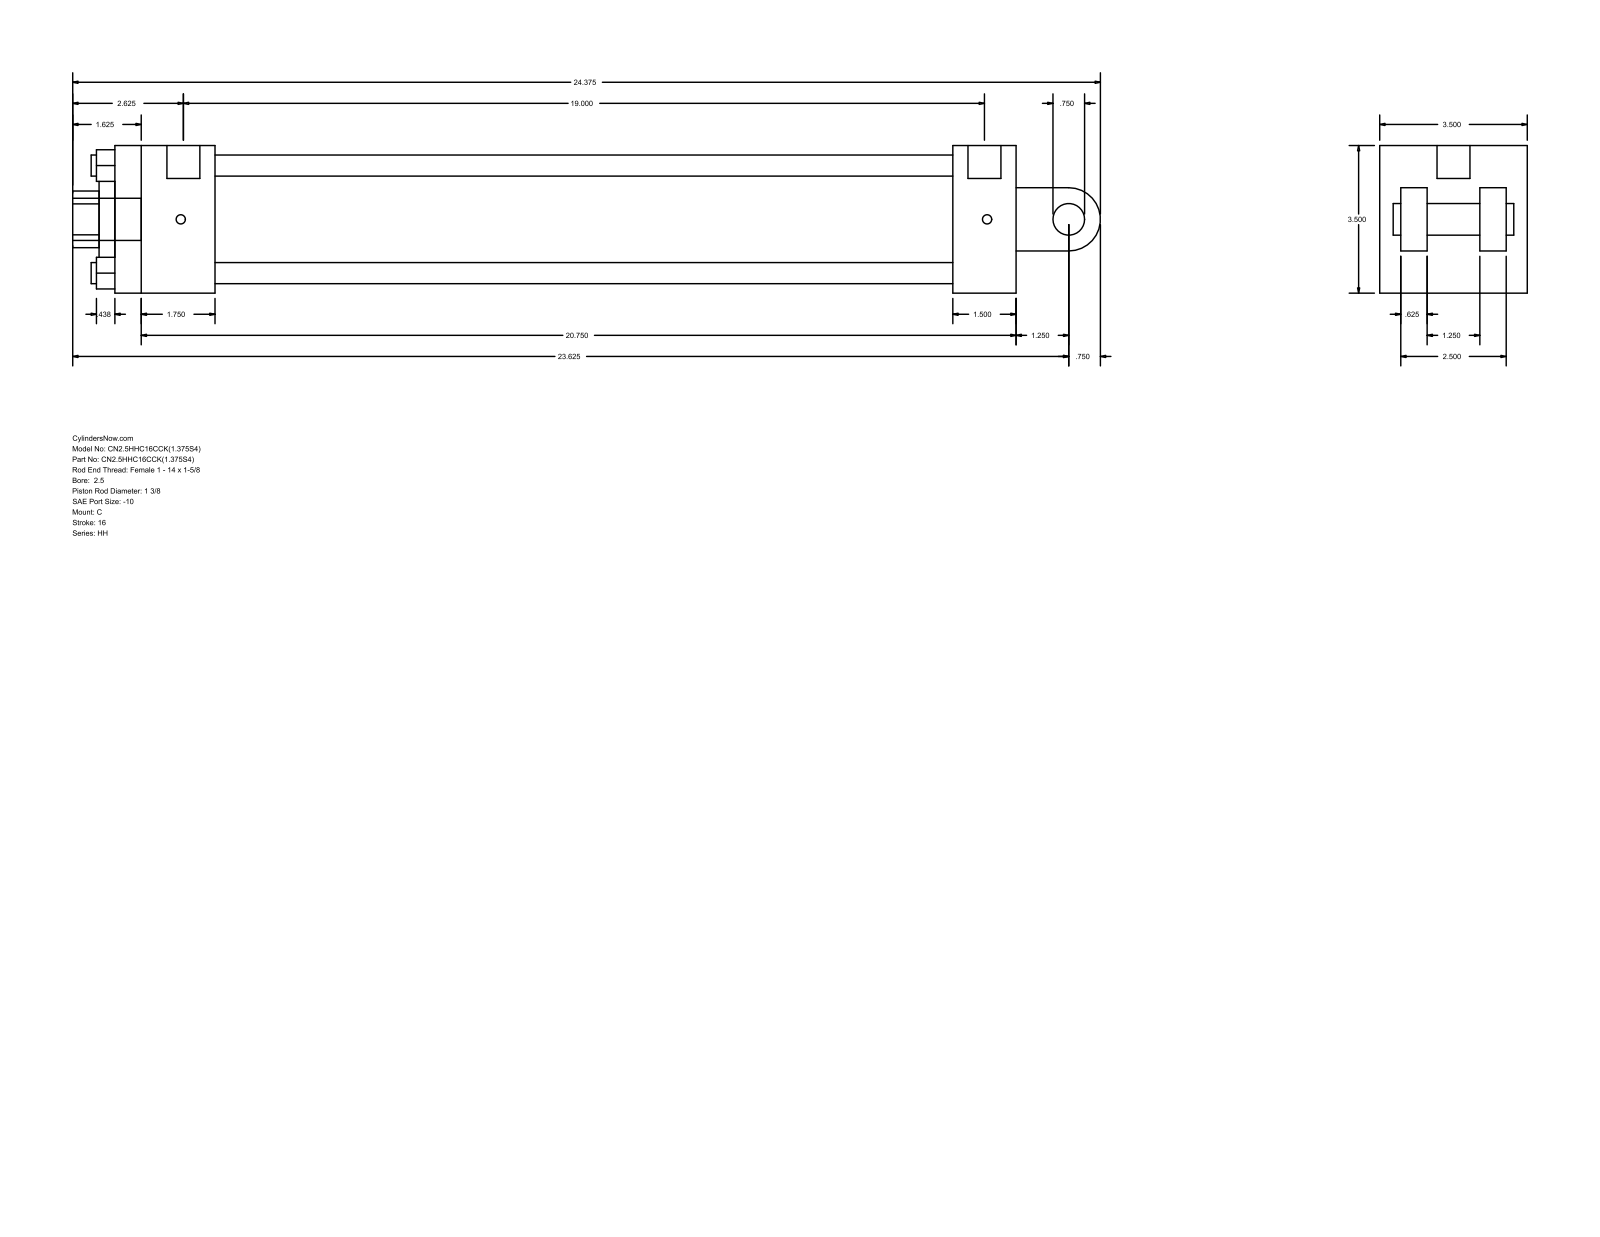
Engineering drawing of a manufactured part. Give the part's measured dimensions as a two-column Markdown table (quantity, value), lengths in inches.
| quantity | value |
| --- | --- |
| part name | HH_C__0250_1.375 |
| STEP written by | GSSL Pune (CONFIG_CONTROL_DESIGN) |
| units | inches |
| bodies | 0 solids, 99 faces (70 planar, 29 cylindrical, 0 other) |
| overall size | 24.375 × 3.5 × 3.5 |
| round holes (diameter × count) | 0.5 × 4, 0.219 × 2, 0.781 × 1, 1.375 × 1, 2 × 1, 2.875 × 1 |
| round bosses / shafts (diameter × count) | 0.219 × 2, 1 × 1, 0.781 × 1, 0.75 × 1 |
| partial cylindrical surfaces (radius × count) | 0.672 × 1, 0.75 × 1 |
| main face-to-face distances | 3.5, 21.375, 1.5, 2.5, 0.625, 0.5, 19.875, 2.375, 17.5, 19 |
| hole center spacings | 1.803, 2.55, 3.606, 0.063 |
